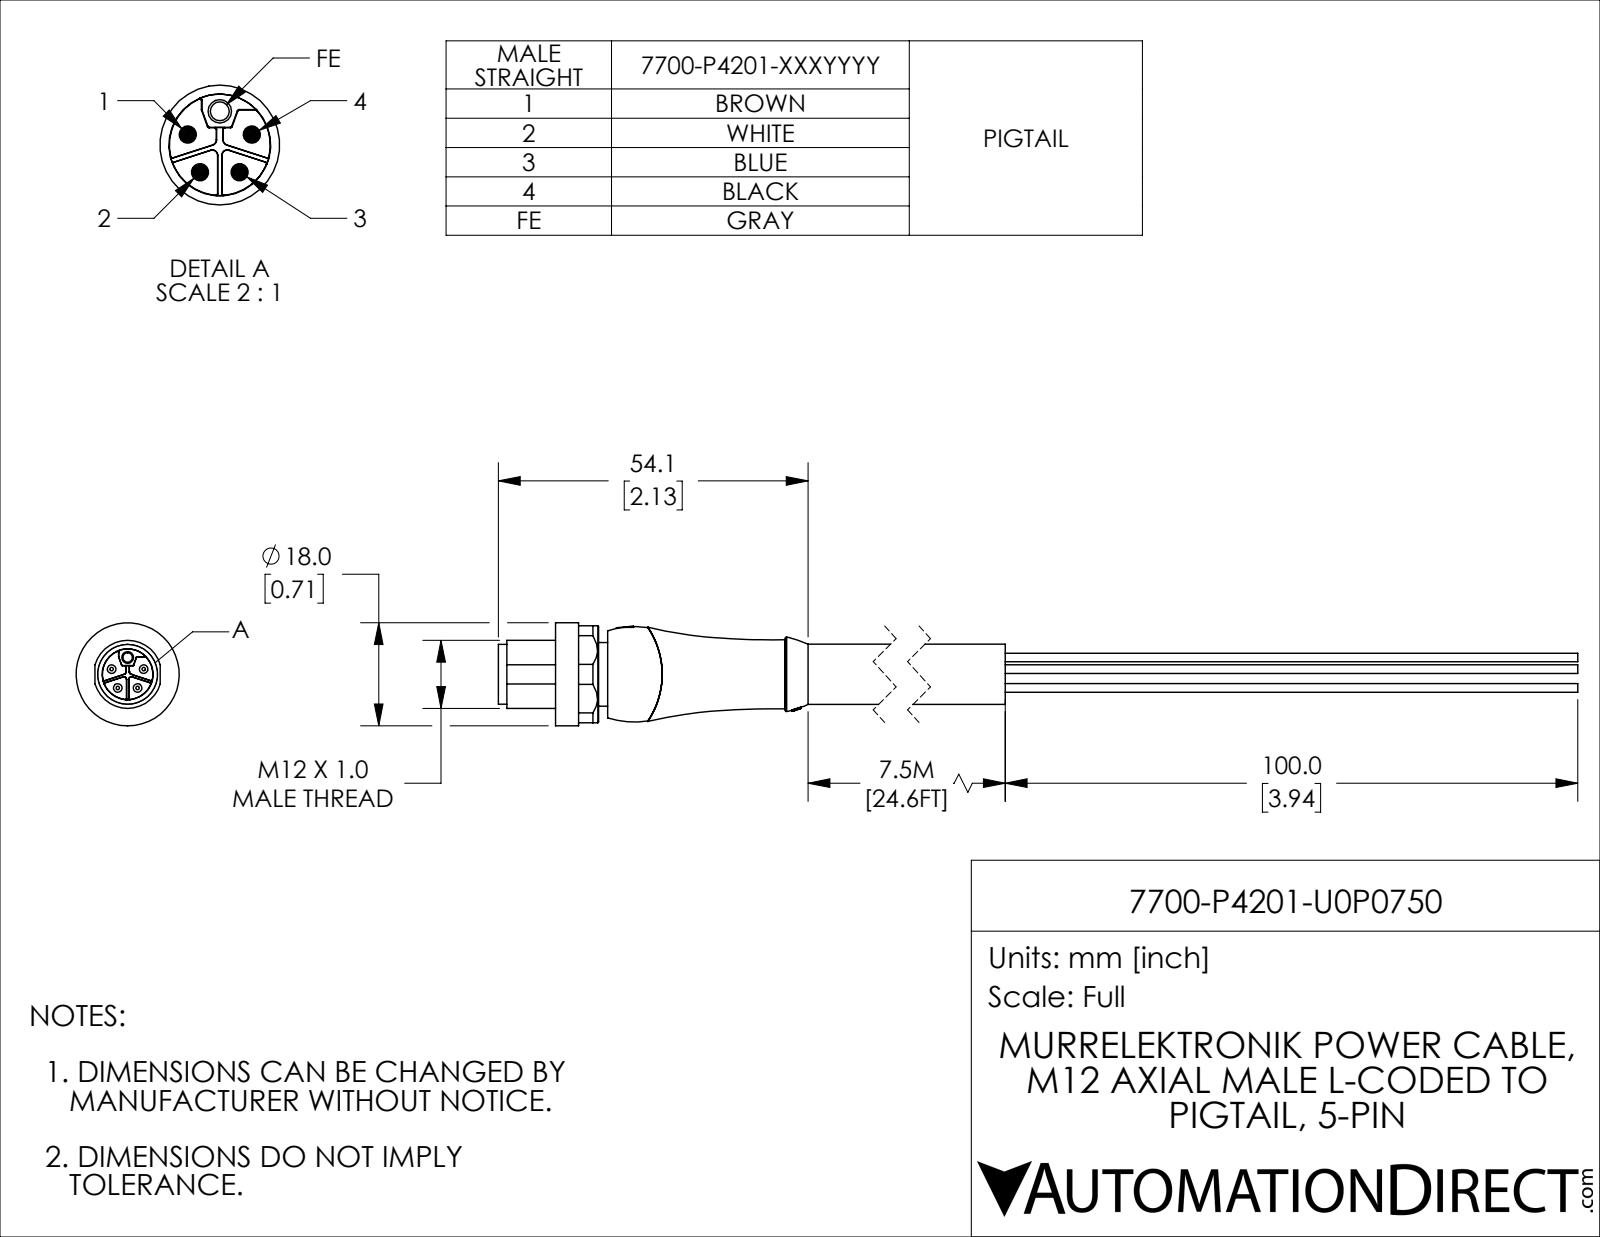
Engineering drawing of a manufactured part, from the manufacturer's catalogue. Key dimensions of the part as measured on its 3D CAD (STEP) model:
Part name (STEP PRODUCT): 7700-P4201-U0P0750
STEP written by: SolidWorks 2021 (CONFIG_CONTROL_DESIGN)
Units: millimetres
Bodies: 1 solid, 190 faces (87 planar, 51 cylindrical, 52 other)
Overall size (bounding box): 254.1 × 18 × 18
Volume: 17 489 mm³ · Surface area: 9 110 mm²
Round holes (diameter × count): ⌀1.65 ×1
Round bosses / shafts (diameter × count): ⌀1.5 ×5, ⌀18 ×1, ⌀11.88 ×1, ⌀11.1 ×1, ⌀10.5 ×1, ⌀10.45 ×1
Partial cylindrical surfaces — rounded edges, fillets, slot ends (radius × count): R0.15 ×6, R1.13 ×1, R8.95 ×1
Main face-to-face distances: 9.1, 1.9, 7.2, 144.1, 136.9, 135, 16.94, 1.2, 8.4, 10.3
